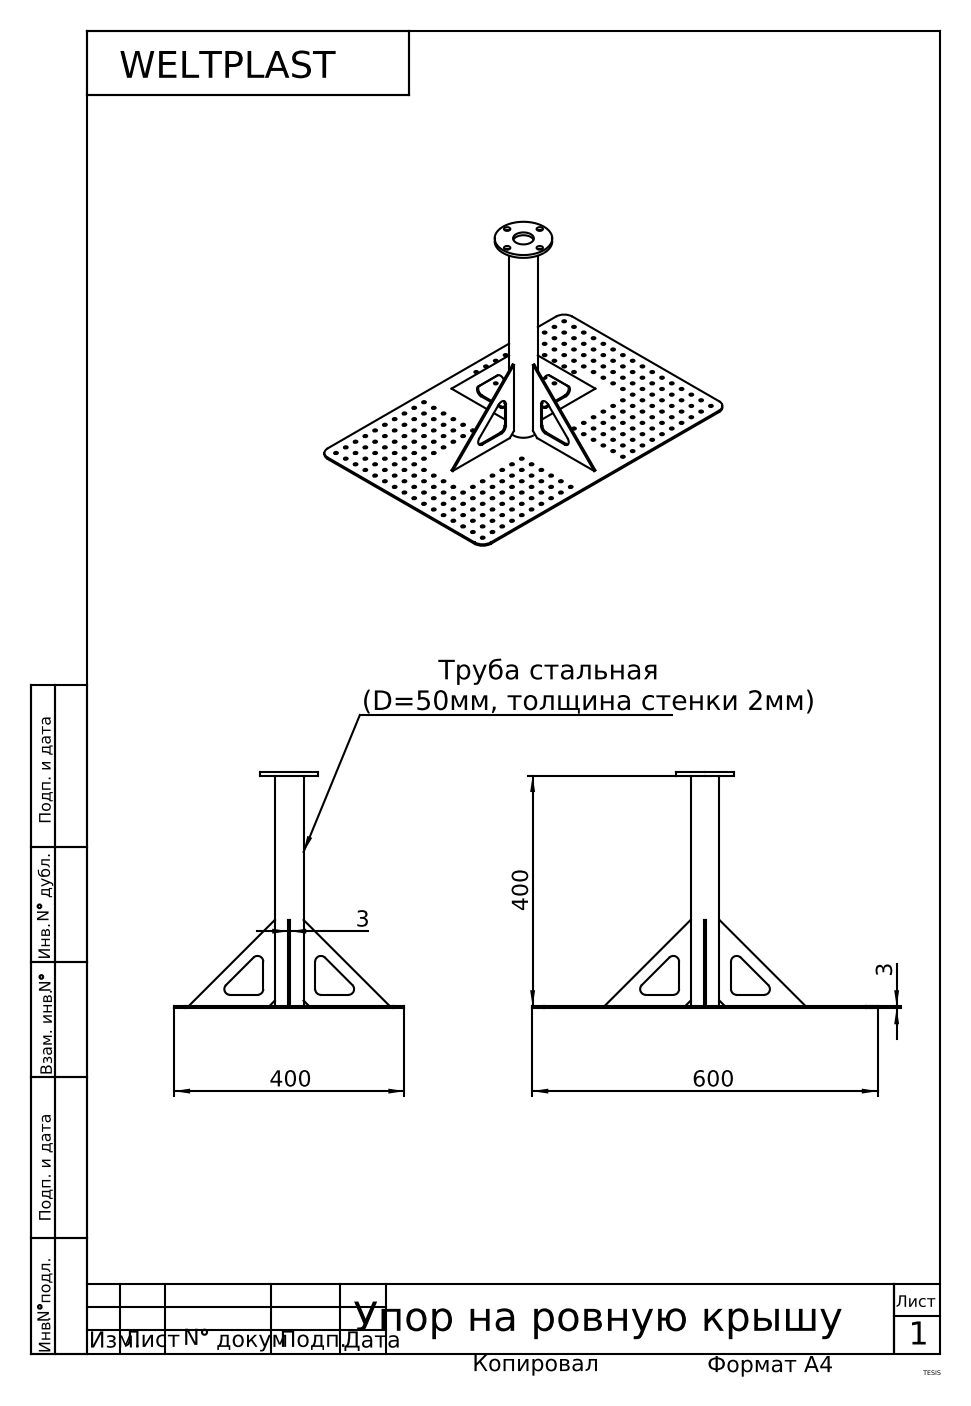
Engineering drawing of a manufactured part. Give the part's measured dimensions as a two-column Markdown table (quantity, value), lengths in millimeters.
| quantity | value |
| --- | --- |
| part name | Основание на крышу; Фланец; Труба (круг); Сборка Упора на ровную крышу. (+1 more) |
| STEP written by | SolidWorks 2017 (AUTOMOTIVE_DESIGN) |
| units | millimeters |
| bodies | 7 solids, 628 faces (46 planar, 582 cylindrical, 0 other) |
| overall size | 600 × 409 × 400 |
| volume | 945 882 mm³ |
| surface area | 693 343 mm² |
| round holes (diameter × count) | 6.4 × 272, 11 × 4, 36 × 1, 40 × 1, 46 × 1 |
| round bosses / shafts (diameter × count) | 100 × 1, 50 × 1 |
| partial cylindrical surfaces (radius × count) | 10 × 12, 20 × 4 |
| main face-to-face distances | 3, 400, 403, 409, 406, 6, 198.5, 201.5, 298.5, 301.5 |
| hole center spacings | 24, 33.94, 48, 53.67, 72, 75.89, 96, 98.95 |
